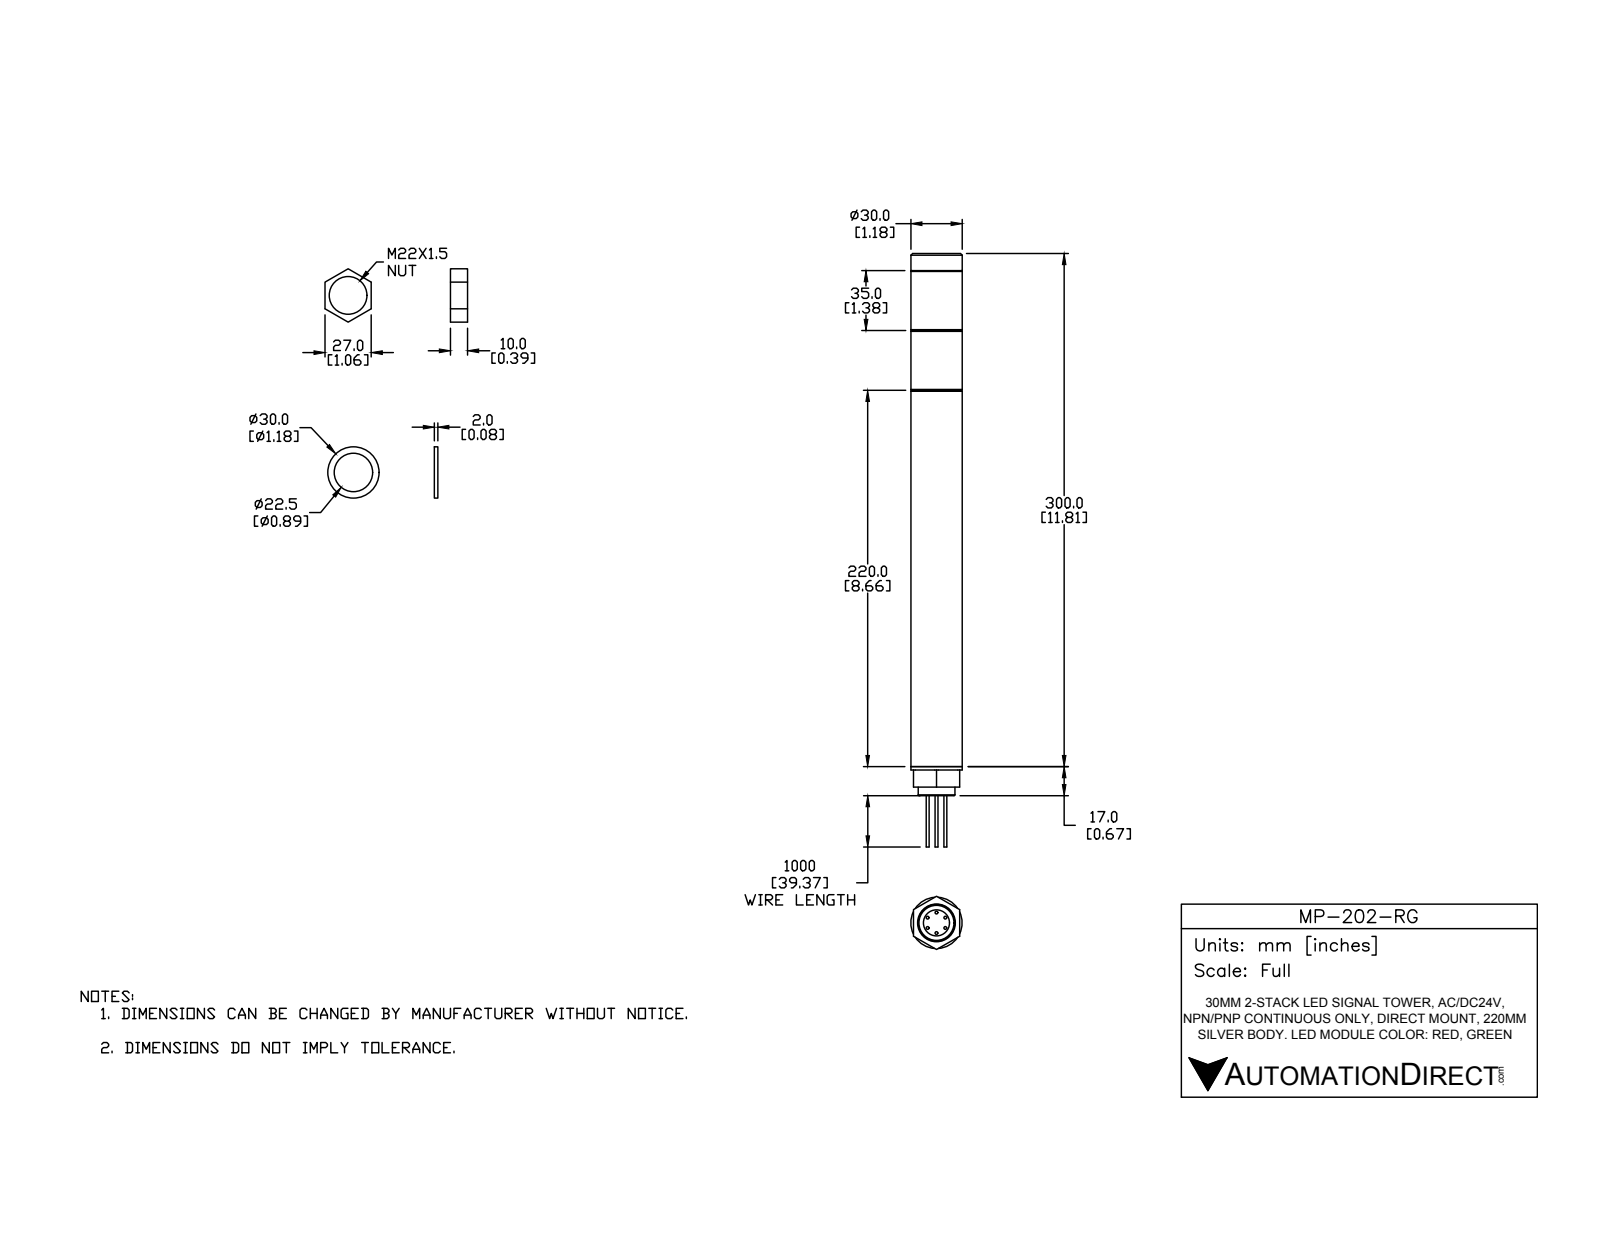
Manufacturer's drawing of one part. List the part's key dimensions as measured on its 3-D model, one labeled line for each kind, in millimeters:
Part name (STEP PRODUCT): MP-202-RG
STEP written by: SolidWorks 2016 (AUTOMOTIVE_DESIGN)
Units: millimetres
Bodies: 13 solids, 103 faces (49 planar, 38 cylindrical, 16 other)
Overall size (bounding box): 347 × 31.18 × 30
Volume: 208 004 mm³ · Surface area: 44 060 mm²
Round holes (diameter × count): ⌀3.2 ×1, ⌀7.7 ×1, ⌀15.3 ×1, ⌀20.7 ×1, ⌀22 ×1
Round bosses / shafts (diameter × count): ⌀1.7 ×6, ⌀30 ×1, ⌀21.5 ×1, ⌀5 ×1
Main face-to-face distances: 35, 70, 222, 257, 45, 302, 220, 255, 290, 10
